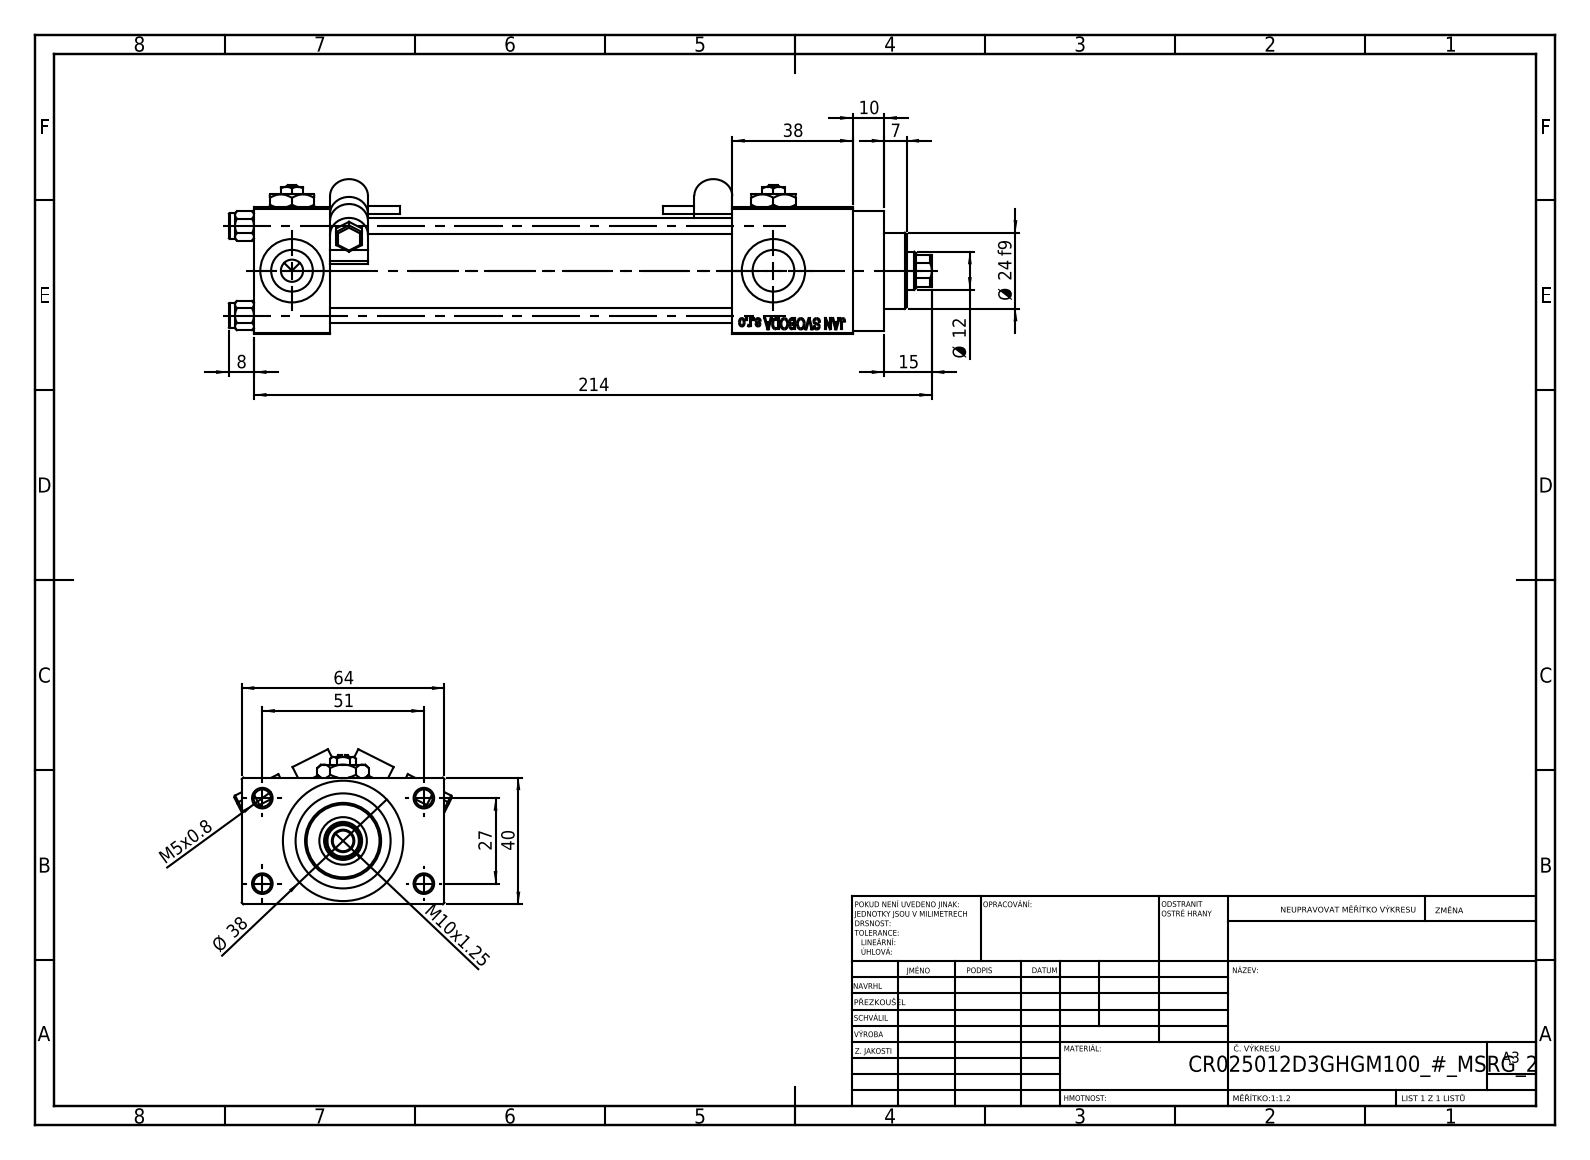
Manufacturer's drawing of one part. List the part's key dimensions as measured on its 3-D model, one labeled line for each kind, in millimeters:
Part name (STEP PRODUCT): V215CR_D_Body; V215_VC_A; NUT_M5_D; MSRF_MSRG1 (+3 more)
STEP written by: SolidWorks 2019 (CONFIG_CONTROL_DESIGN)
Units: millimetres
Bodies: 15 solids, 1265 faces (578 planar, 127 cylindrical, 560 other)
Overall size (bounding box): 222 × 68.71 × 48.93
Volume: 216 003 mm³ · Surface area: 90 074 mm²
Round holes (diameter × count): ⌀20 ×5, ⌀5 ×4, ⌀5.5 ×4, ⌀13.16 ×4, ⌀7 ×3, ⌀6.5 ×1, ⌀12 ×1, ⌀15 ×1, ⌀25 ×1, ⌀30 ×1
Round bosses / shafts (diameter × count): ⌀8 ×4, ⌀5 ×2, ⌀2.5 ×2, ⌀38 ×1, ⌀31 ×1, ⌀24 ×1
Partial cylindrical surfaces — rounded edges, fillets, slot ends (radius × count): R0.5 ×12, R6 ×4, R5.5 ×1
Main face-to-face distances: 40, 12, 127, 24, 151, 52, 38, 165, 189, 64
Hole centre spacings: 11.37, 20.01, 28.3, 28.85, 29.89, 39.66, 48.34, 27
